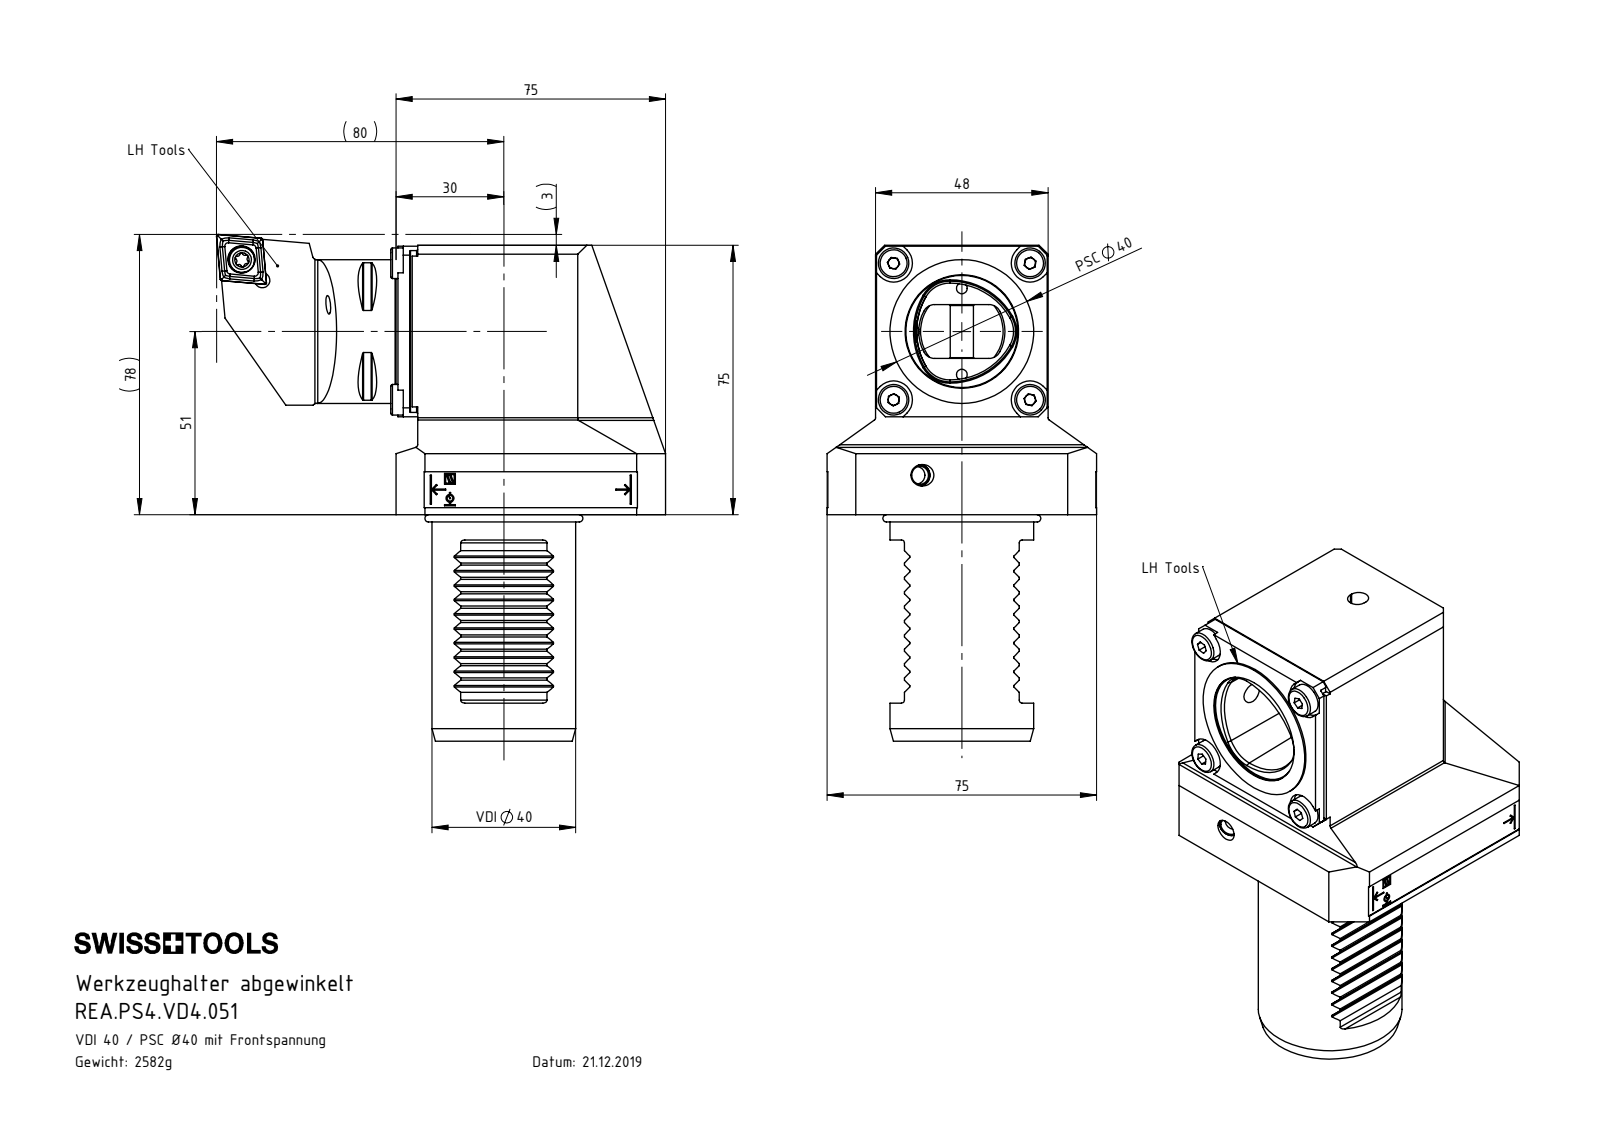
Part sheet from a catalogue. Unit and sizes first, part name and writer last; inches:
Units: inches
Overall size (bounding box): 5.433 × 3.012 × 2.953
Round holes (diameter × count): ⌀0.197 ×5, ⌀0.098 ×4, ⌀0.165 ×4, ⌀0.217 ×4, ⌀0.118 ×2, ⌀0.13 ×2, ⌀0.236 ×2, ⌀0.512 ×2, ⌀0.551 ×2, ⌀0.157 ×1, ⌀0.276 ×1, ⌀0.669 ×1
Round bosses / shafts (diameter × count): ⌀0.335 ×4, ⌀0.197 ×4, ⌀0.217 ×2, ⌀0.118 ×2, ⌀1.575 ×1, ⌀1.563 ×1, ⌀1.488 ×1, ⌀1.457 ×1
Partial cylindrical surfaces — rounded edges, fillets, slot ends (radius × count): R0.012 ×20, R0.031 ×9, R0.138 ×4, R0.207 ×4, R0.008 ×2, R0.108 ×2, R0.118 ×2, R0.354 ×1
Main face-to-face distances: 2.953, 1.89, 0.118, 2.835, 0.236, 0.111, 1.654, 0.524, 2.413, 0.557
Hole centre spacings: 0.797, 1.058, 1.431, 1.496, 0.472, 0.5, 0.621, 0.649
Volume: 18.35 in³ · Surface area: 128.8 in²
Bodies: 25 solids, 922 faces (389 planar, 218 cylindrical, 315 other)
Part name (STEP PRODUCT): U40-PS4.048.006; ISO 4762 - M16 x 65; VD4-ER1.014.010; DIN 3771 - 37x1.5 (+8 more)
STEP written by: SolidWorks 2022 (AUTOMOTIVE_DESIGN)
